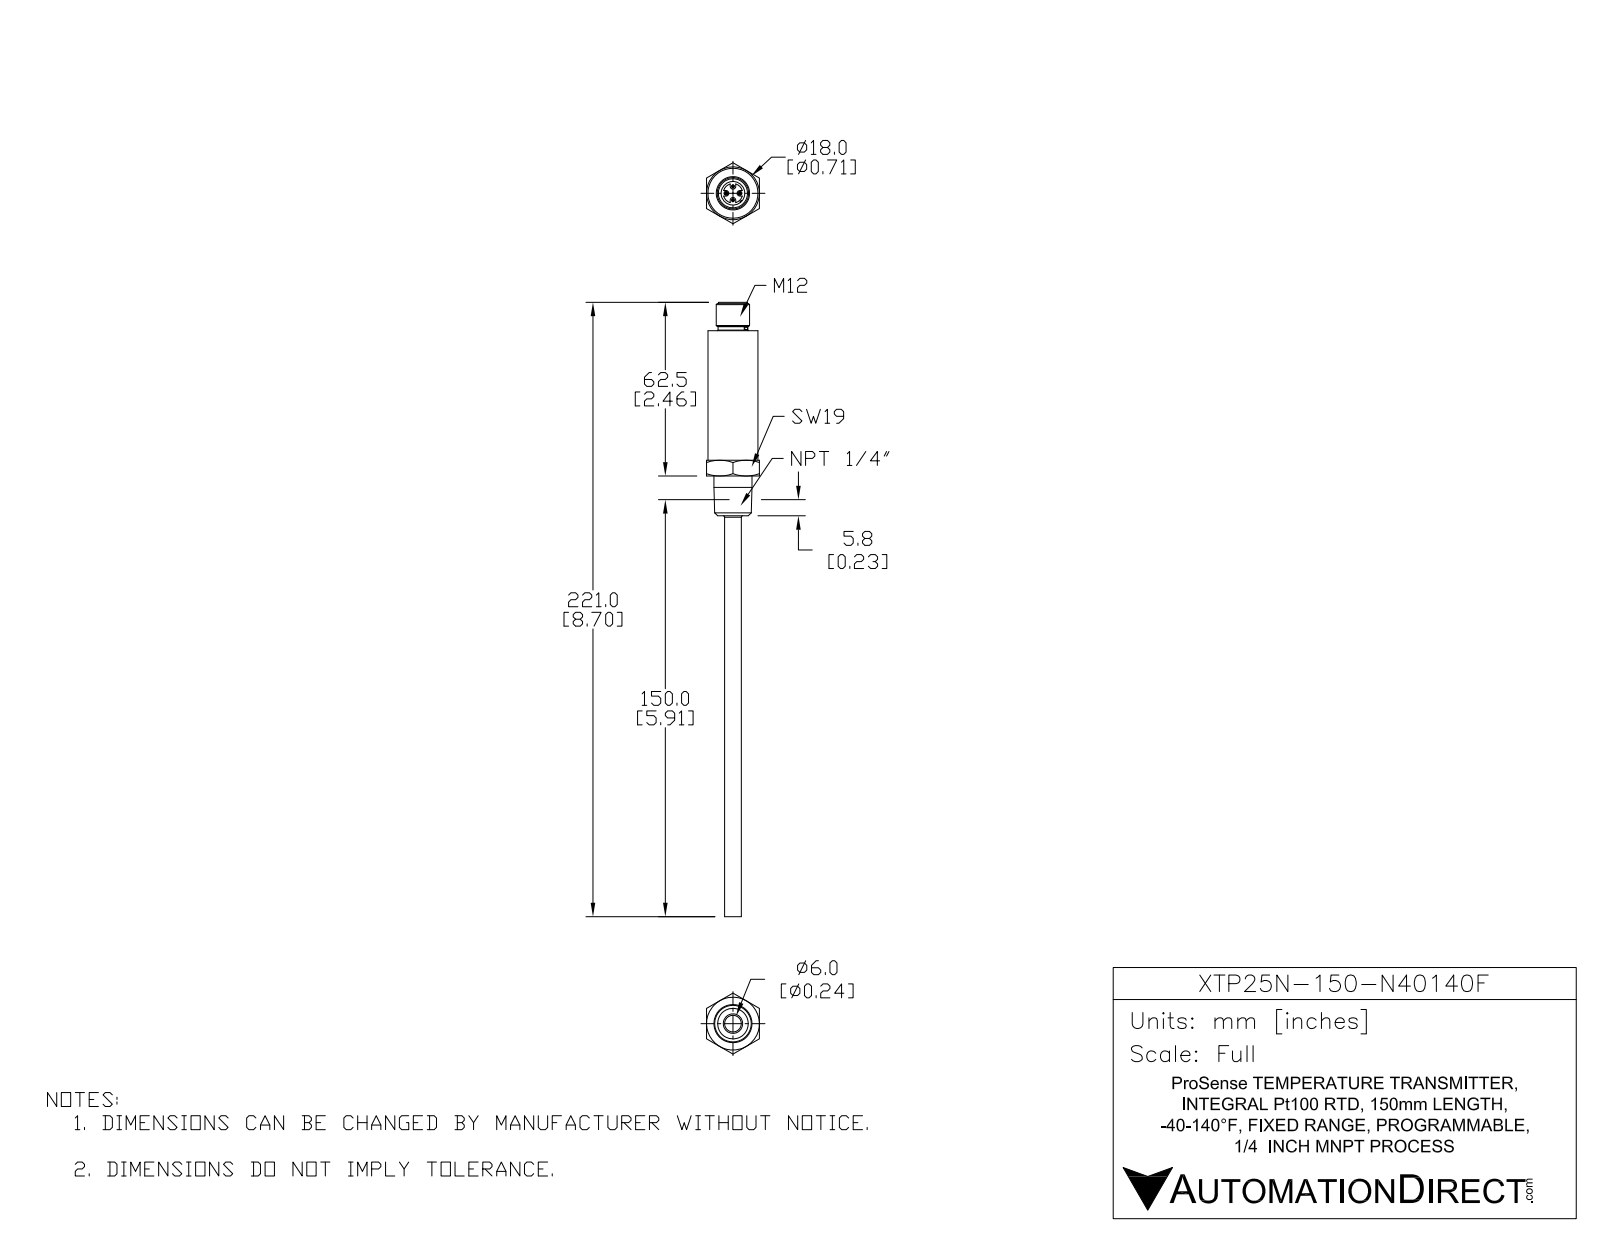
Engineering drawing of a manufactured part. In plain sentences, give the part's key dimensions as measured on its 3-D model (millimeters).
The part is named "XTP25N-150-N40140F". Its 3-D file was written by "SolidWorks 2015 (AUTOMOTIVE_DESIGN)". It is 1 solid with 117 faces: 43 planar, 34 cylindrical and 40 other. Overall it measures 221 by 21.94 by 19 millimeters. Its volume is 20 060 cubic millimeters and its surface area 7 889 square millimeters. Round holes: 1 of diameter 4, 1 of diameter 8.5. Round bosses or shafts: 4 of diameter 1.02, 1 of diameter 18, 1 of diameter 13.72, 1 of diameter 12, 1 of diameter 10.7, 1 of diameter 10.5, 1 of diameter 6. Partial cylindrical surfaces (rounded edges, fillets, slot ends): 4 of radius 1, 1 of radius 3.5, 1 of radius 4.25. The main face-to-face distances are 19, 52.3, 14.3, 66.6, 20, 5.7, 46.6, 76.8, 62.5, 56.8.
